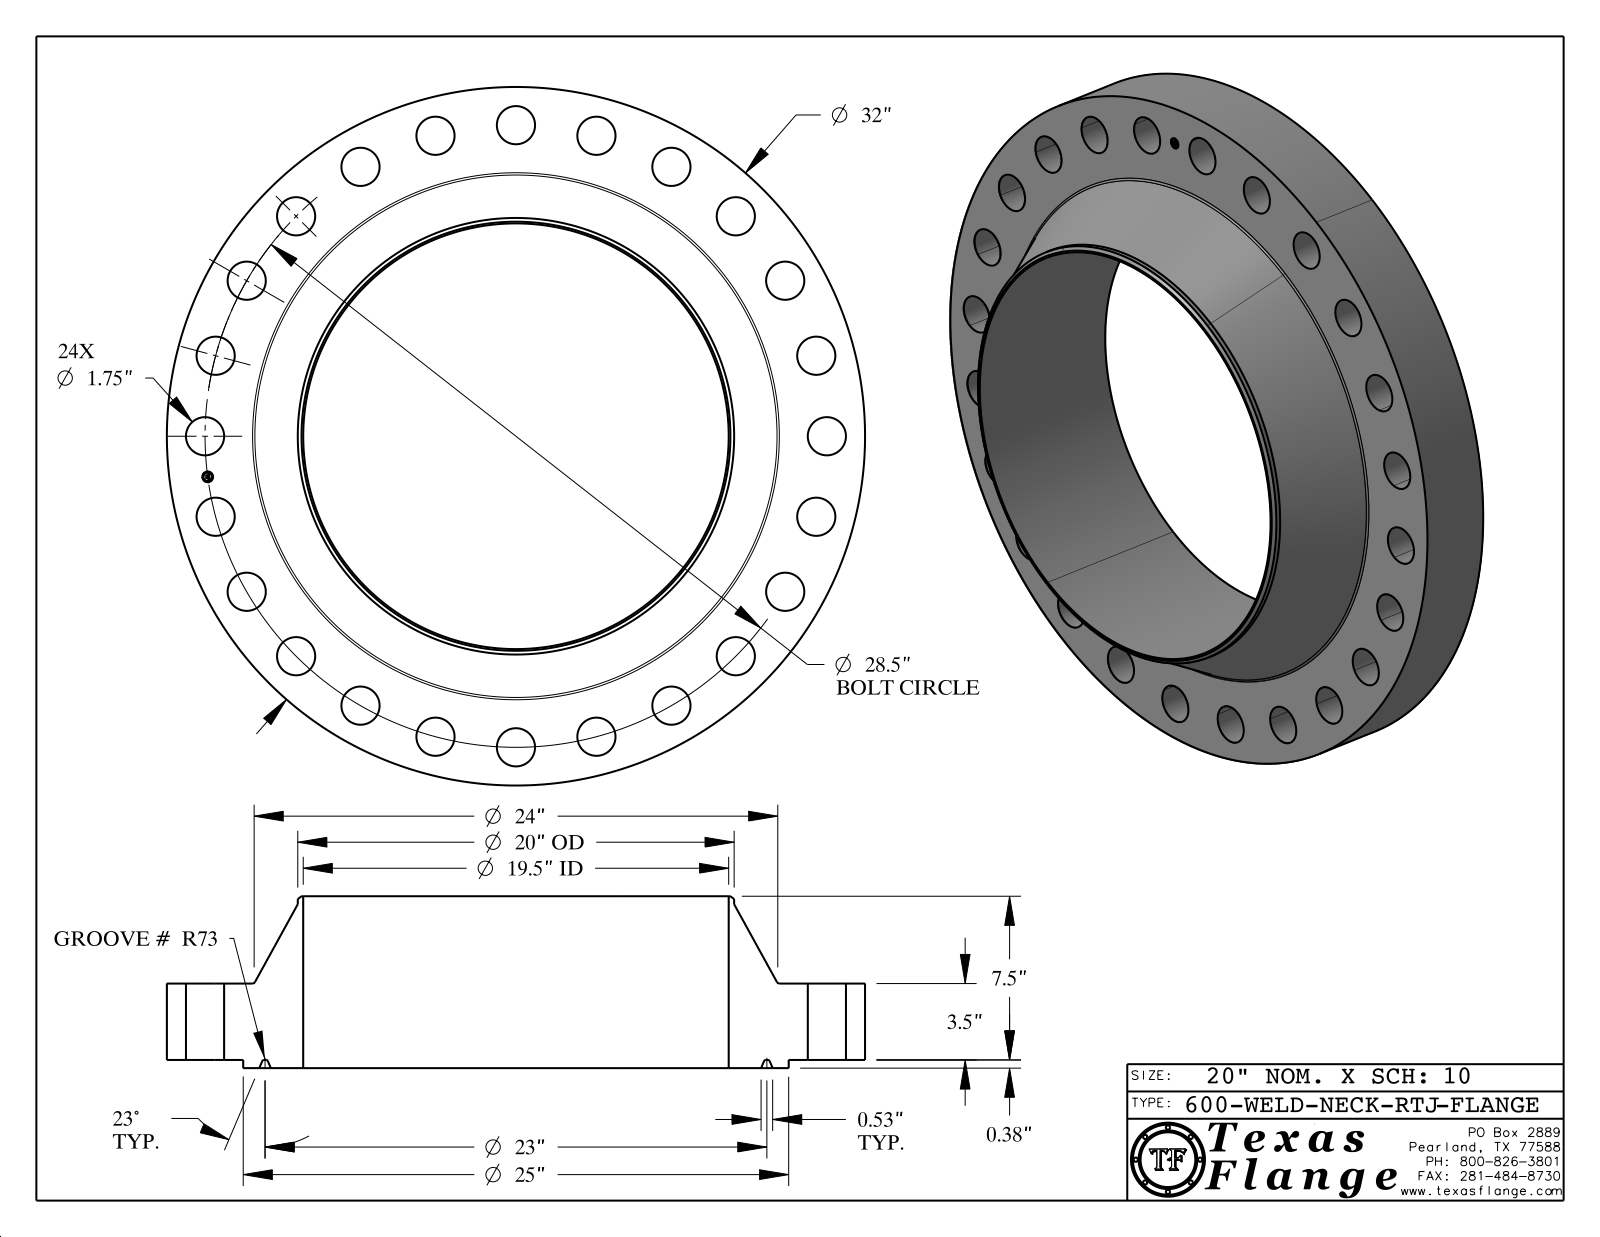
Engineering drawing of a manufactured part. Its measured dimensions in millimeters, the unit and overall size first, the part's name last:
Units: millimetres
Overall size (bounding box): 812.8 × 812.8 × 200
Round holes (diameter × count): ⌀44.5 ×24, ⌀12.6 ×1, ⌀495.3 ×1
Round bosses / shafts (diameter × count): ⌀0.8 ×8, ⌀812.8 ×1, ⌀635 ×1, ⌀508 ×1, ⌀9.9 ×1
Main face-to-face distances: 88.9, 9.5, 98.4, 200, 190.5, 101.6, 0.4, 98, 88.5, 102
Hole centre spacings: 362, 94.5, 187.4, 626.9, 668.8, 699.2, 511.9, 277
Volume: 31 690 000 mm³ · Surface area: 1 562 000 mm²
Bodies: 1 solid, 461 faces (371 planar, 76 cylindrical, 14 other)
Part name (STEP PRODUCT): 600-WELD-NECK-RTJ
STEP written by: CATIA V5 STEP AP214 (AUTOMOTIVE_DESIGN)
